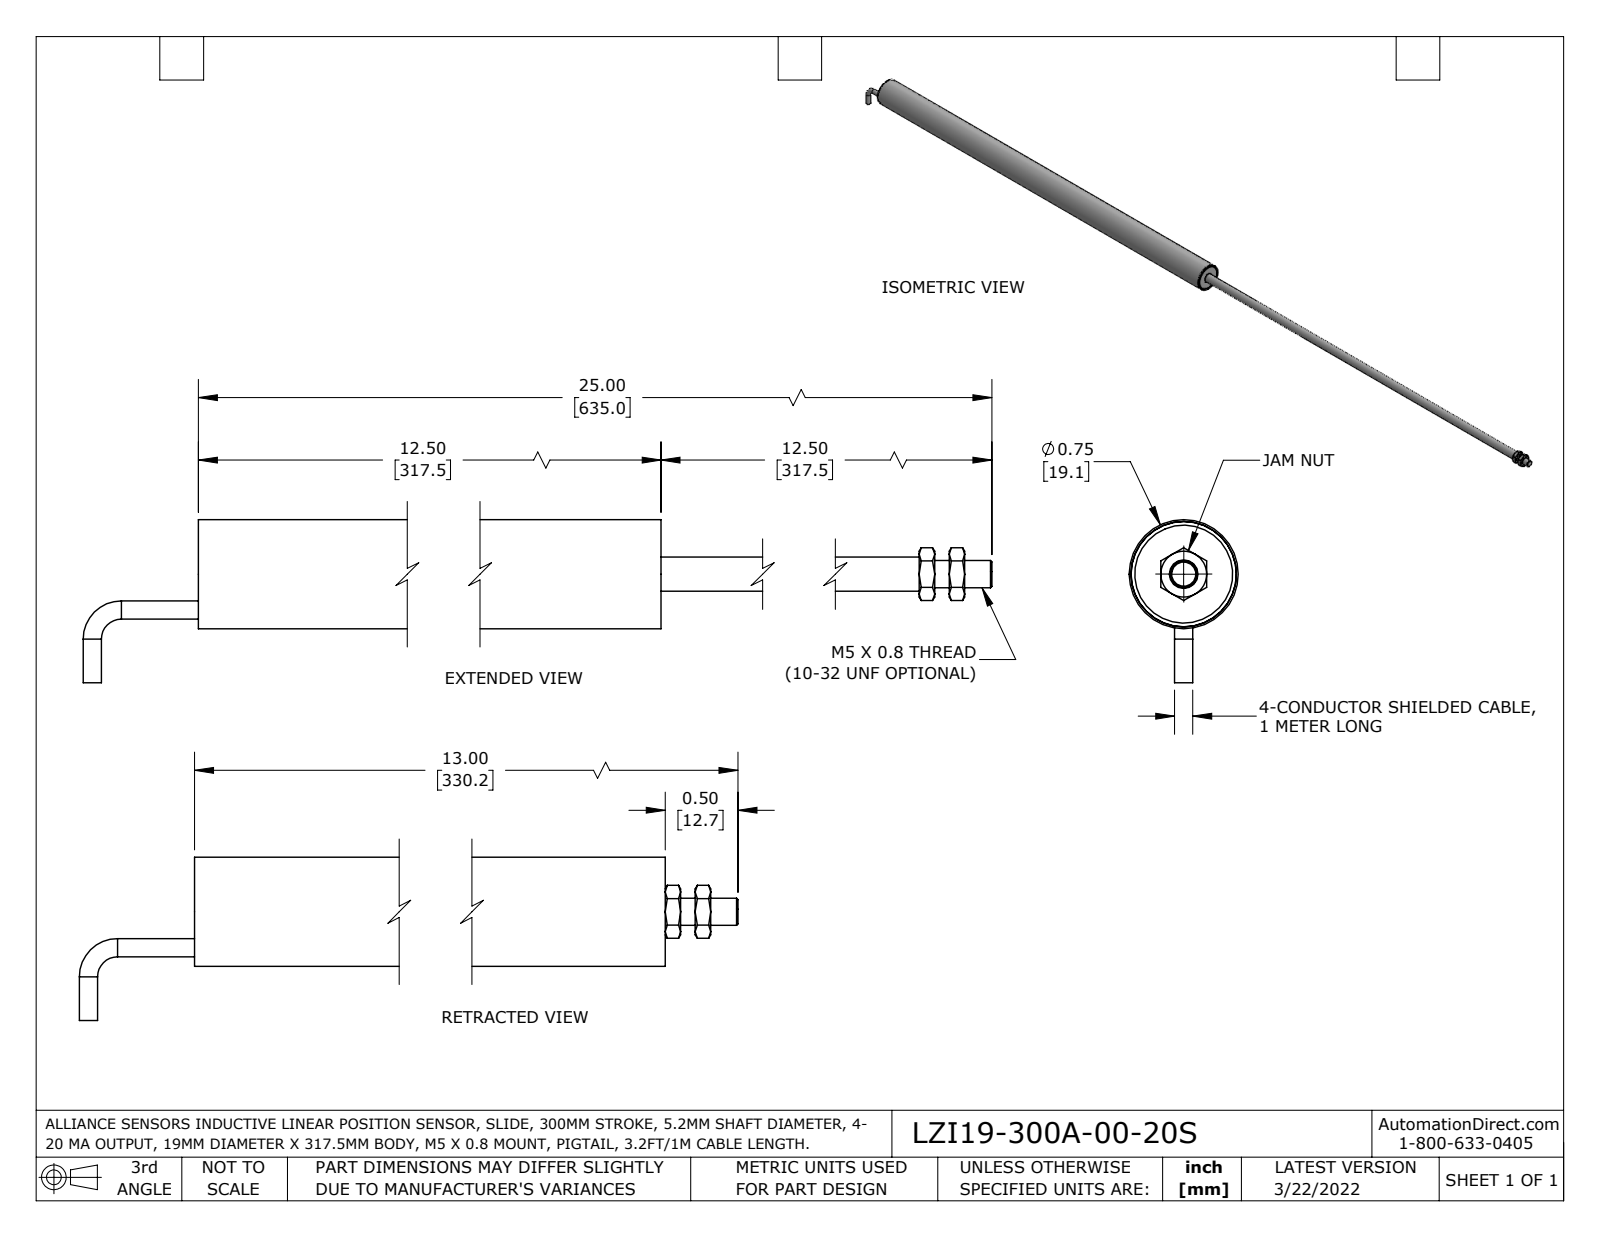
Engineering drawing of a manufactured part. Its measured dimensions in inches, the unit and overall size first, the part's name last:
Units: inches
Overall size (bounding box): 25.793 × 1.121 × 0.75
Round holes (diameter × count): ⌀0.165 ×1, ⌀0.188 ×1, ⌀0.197 ×1, ⌀0.234 ×1, ⌀0.281 ×1, ⌀0.68 ×1, ⌀0.725 ×1
Round bosses / shafts (diameter × count): ⌀0.125 ×2, ⌀0.75 ×1, ⌀0.723 ×1, ⌀0.278 ×1, ⌀0.187 ×1
Partial cylindrical surfaces — rounded edges, fillets, slot ends (radius × count): R0.052 ×1
Main face-to-face distances: 0.06, 12.42, 0.08, 12.36, 12.48, 0.315, 0.206, 0.106, 0.374, 12.5
Volume: 1.847 in³ · Surface area: 104.6 in²
Bodies: 10 solids, 137 faces (42 planar, 44 cylindrical, 51 other)
Part name (STEP PRODUCT): LZI19-300A-00-20S; 3100-0076_B18.2.4.5M - Hex jam nut, M5 x 0.8 --D-N; 3120-0008-06_-12; 3120-0009-06_-12 (+6 more)
STEP written by: SolidWorks 2021 (AUTOMOTIVE_DESIGN)
